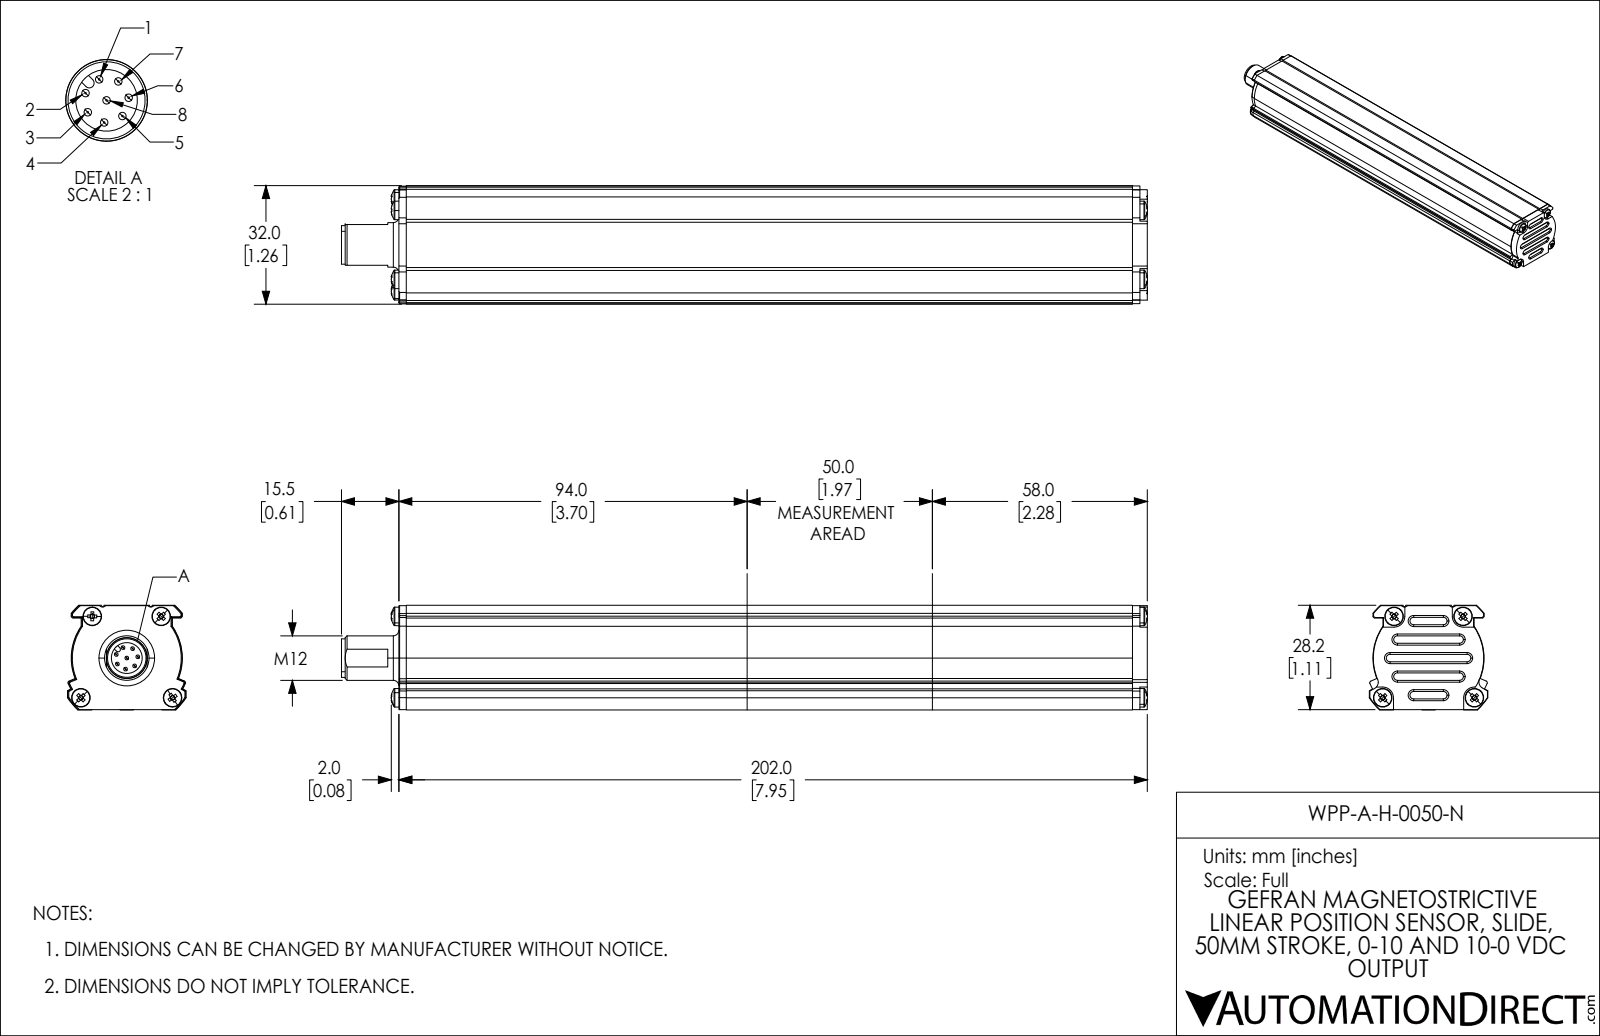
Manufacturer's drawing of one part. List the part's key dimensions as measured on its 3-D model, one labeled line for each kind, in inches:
Part name (STEP PRODUCT): WPP-A-H-0050-N
STEP written by: SolidWorks 2021 (CONFIG_CONTROL_DESIGN)
Units: inches
Bodies: 20 solids, 605 faces (301 planar, 131 cylindrical, 173 other)
Overall size (bounding box): 8.565 × 1.26 × 1.112
Volume: 9.868 in³ · Surface area: 59.4 in²
Round holes (diameter × count): ⌀0.102 ×5, ⌀0.091 ×4, ⌀0.276 ×1, ⌀0.327 ×1, ⌀0.37 ×1
Round bosses / shafts (diameter × count): ⌀0.039 ×8, ⌀0.197 ×4, ⌀0.472 ×1, ⌀0.409 ×1, ⌀0.376 ×1, ⌀0.315 ×1
Partial cylindrical surfaces — rounded edges, fillets, slot ends (radius × count): R0.02 ×8, R0.114 ×4, R0.016 ×2, R0.039 ×2, R0.073 ×2, R0.026 ×1, R0.079 ×1, R0.587 ×1
Main face-to-face distances: 1.102, 1.112, 7.717, 0.079, 7.795, 0.976, 0.967, 0.136, 0.146, 1.114
Hole centre spacings: 0.644, 0.575, 0.873, 1.215, 0.732, 0.872, 0.974, 0.975
